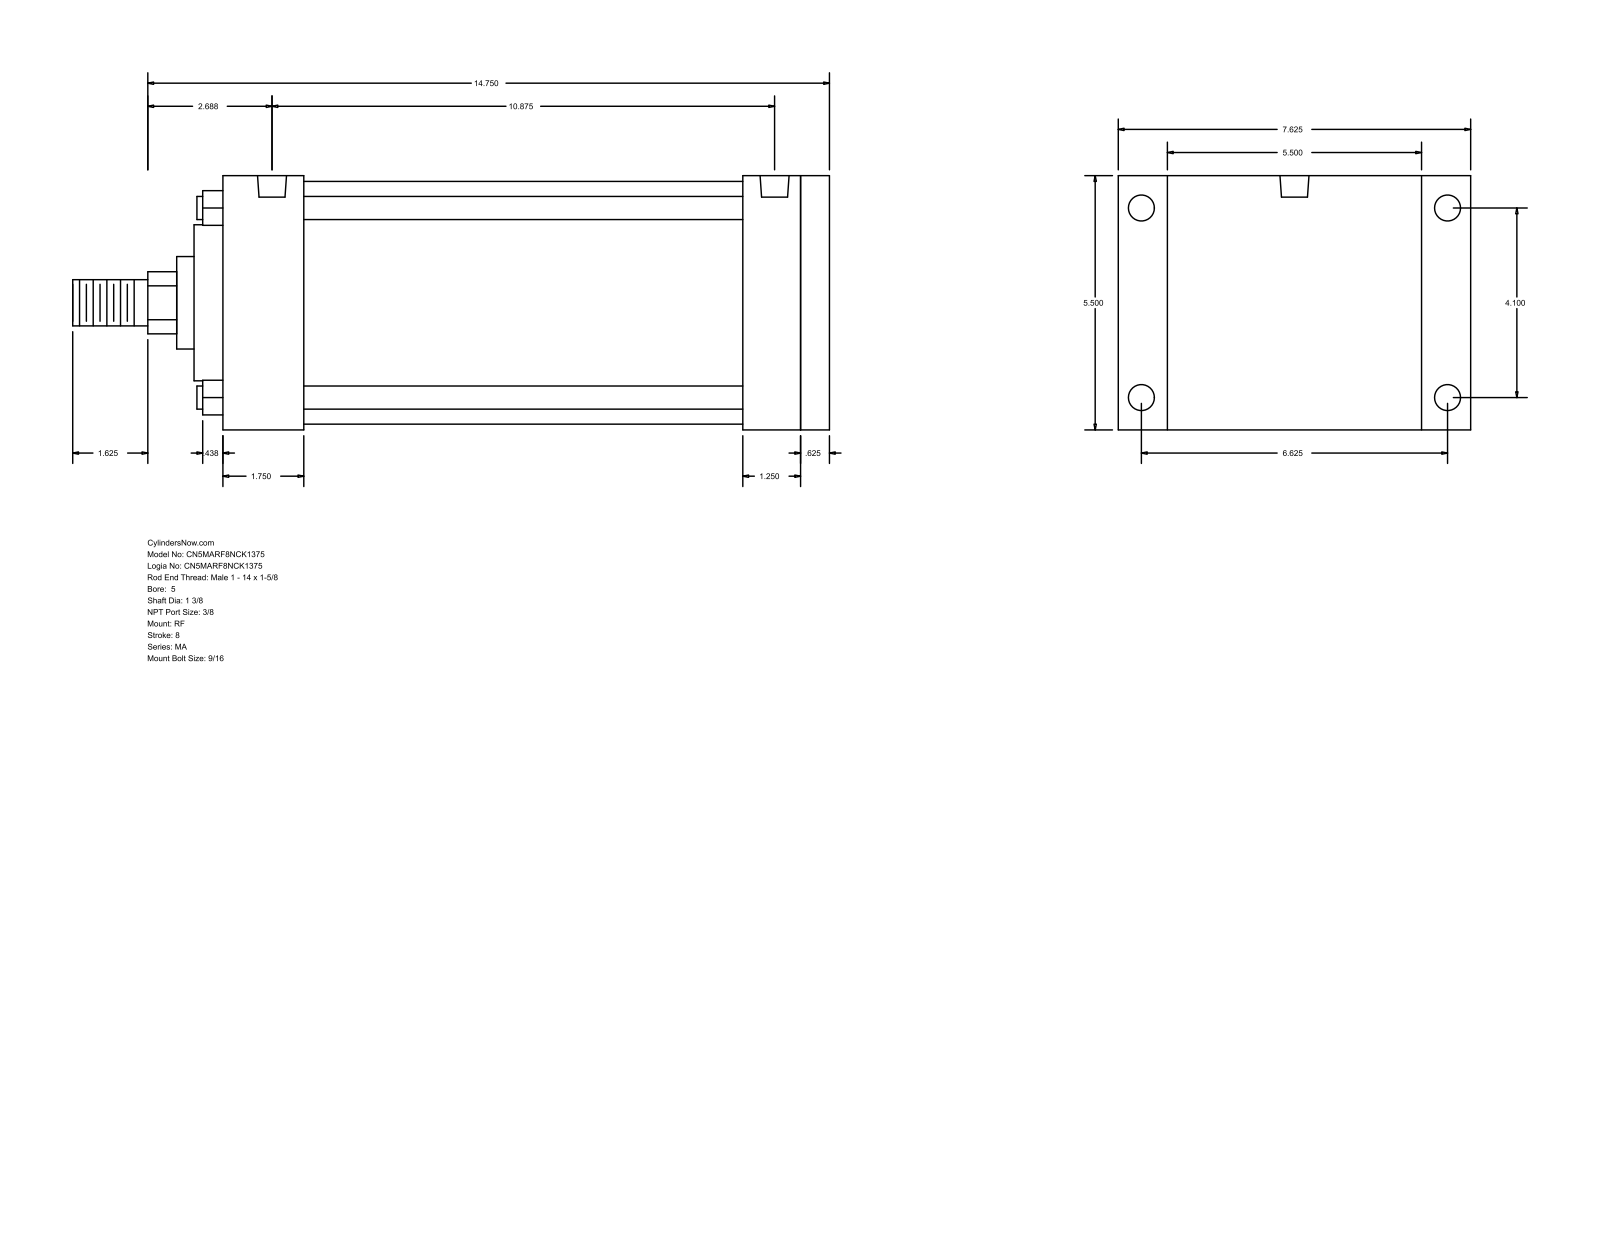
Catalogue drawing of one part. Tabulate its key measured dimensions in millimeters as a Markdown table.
| quantity | value |
| --- | --- |
| part name | MA_RF__0500_1.375 |
| STEP written by | GSSL Pune (CONFIG_CONTROL_DESIGN) |
| units | millimeters |
| bodies | 0 solids, 94 faces (65 planar, 29 cylindrical, 0 other) |
| overall size | 415.93 × 193.68 × 139.7 |
| round holes (diameter × count) | 11.11 × 4, 14.29 × 4, 15.93 × 2 |
| round bosses / shafts (diameter × count) | 12.7 × 4, 133.35 × 1, 85.72 × 1, 50.8 × 1, 34.92 × 1, 25.4 × 1 |
| partial cylindrical surfaces (radius × count) | 17.06 × 1 |
| main face-to-face distances | 139.7, 333.38, 15.88, 317.5, 44.45, 273.05, 288.93, 285.75, 241.3, 31.75 |
| hole center spacings | 104.14, 168.28, 197.9, 266.7, 4.76, 4.77, 271.46, 271.47 |
